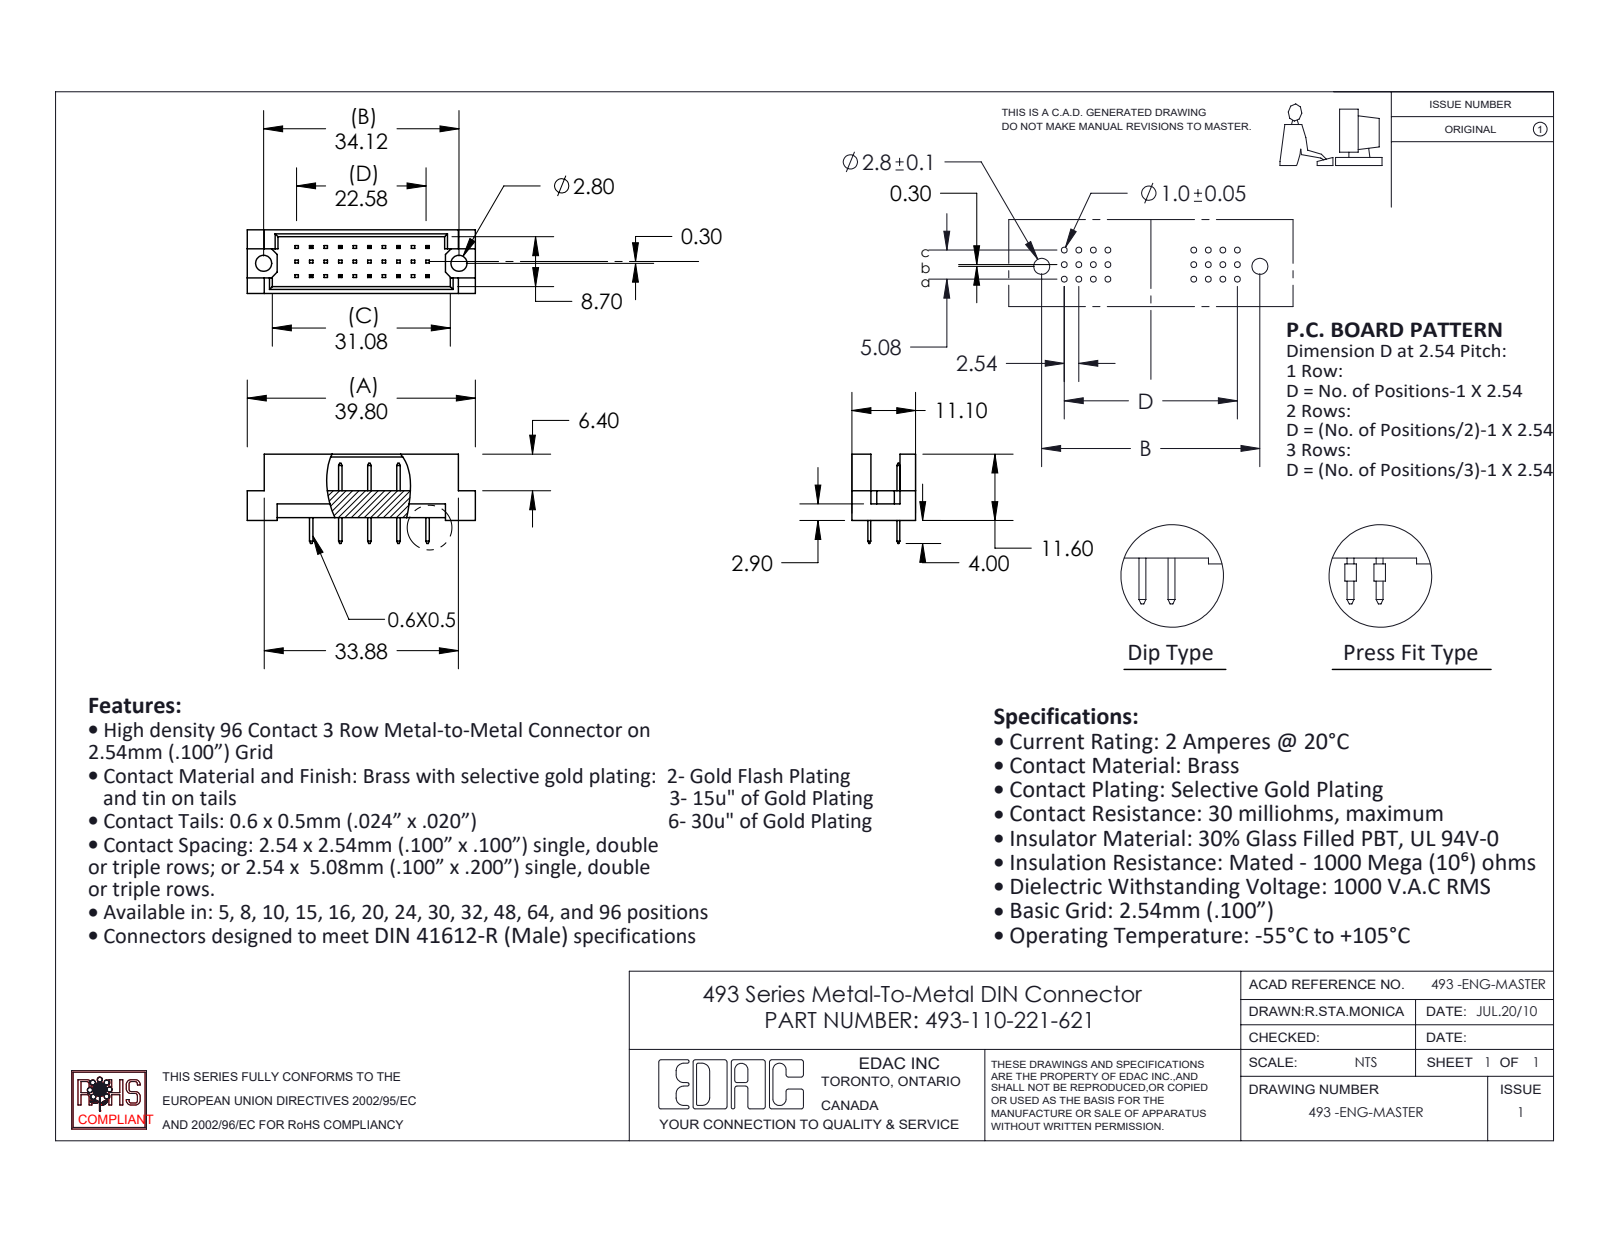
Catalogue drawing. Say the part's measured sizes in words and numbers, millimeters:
The part is named "493-290_21; 493 Part_30; 493-110-221-621". Its 3-D file was written by "SolidWorks 2020 (CONFIG_CONTROL_DESIGN)". It is 11 solids with 312 faces: 308 planar, 4 cylindrical and 0 other. Overall it measures 39.8 by 15.6 by 11.1 millimeters. Its volume is 2 414 cubic millimeters and its surface area 3 042 square millimeters. Round holes: 2 of diameter 2.8. The main face-to-face distances are 1.2, 9.9, 11.1, 5.08, 8.7, 0.5, 4.7, 2.76, 3.26, 7.84. The hole center spacings are 34.12.
